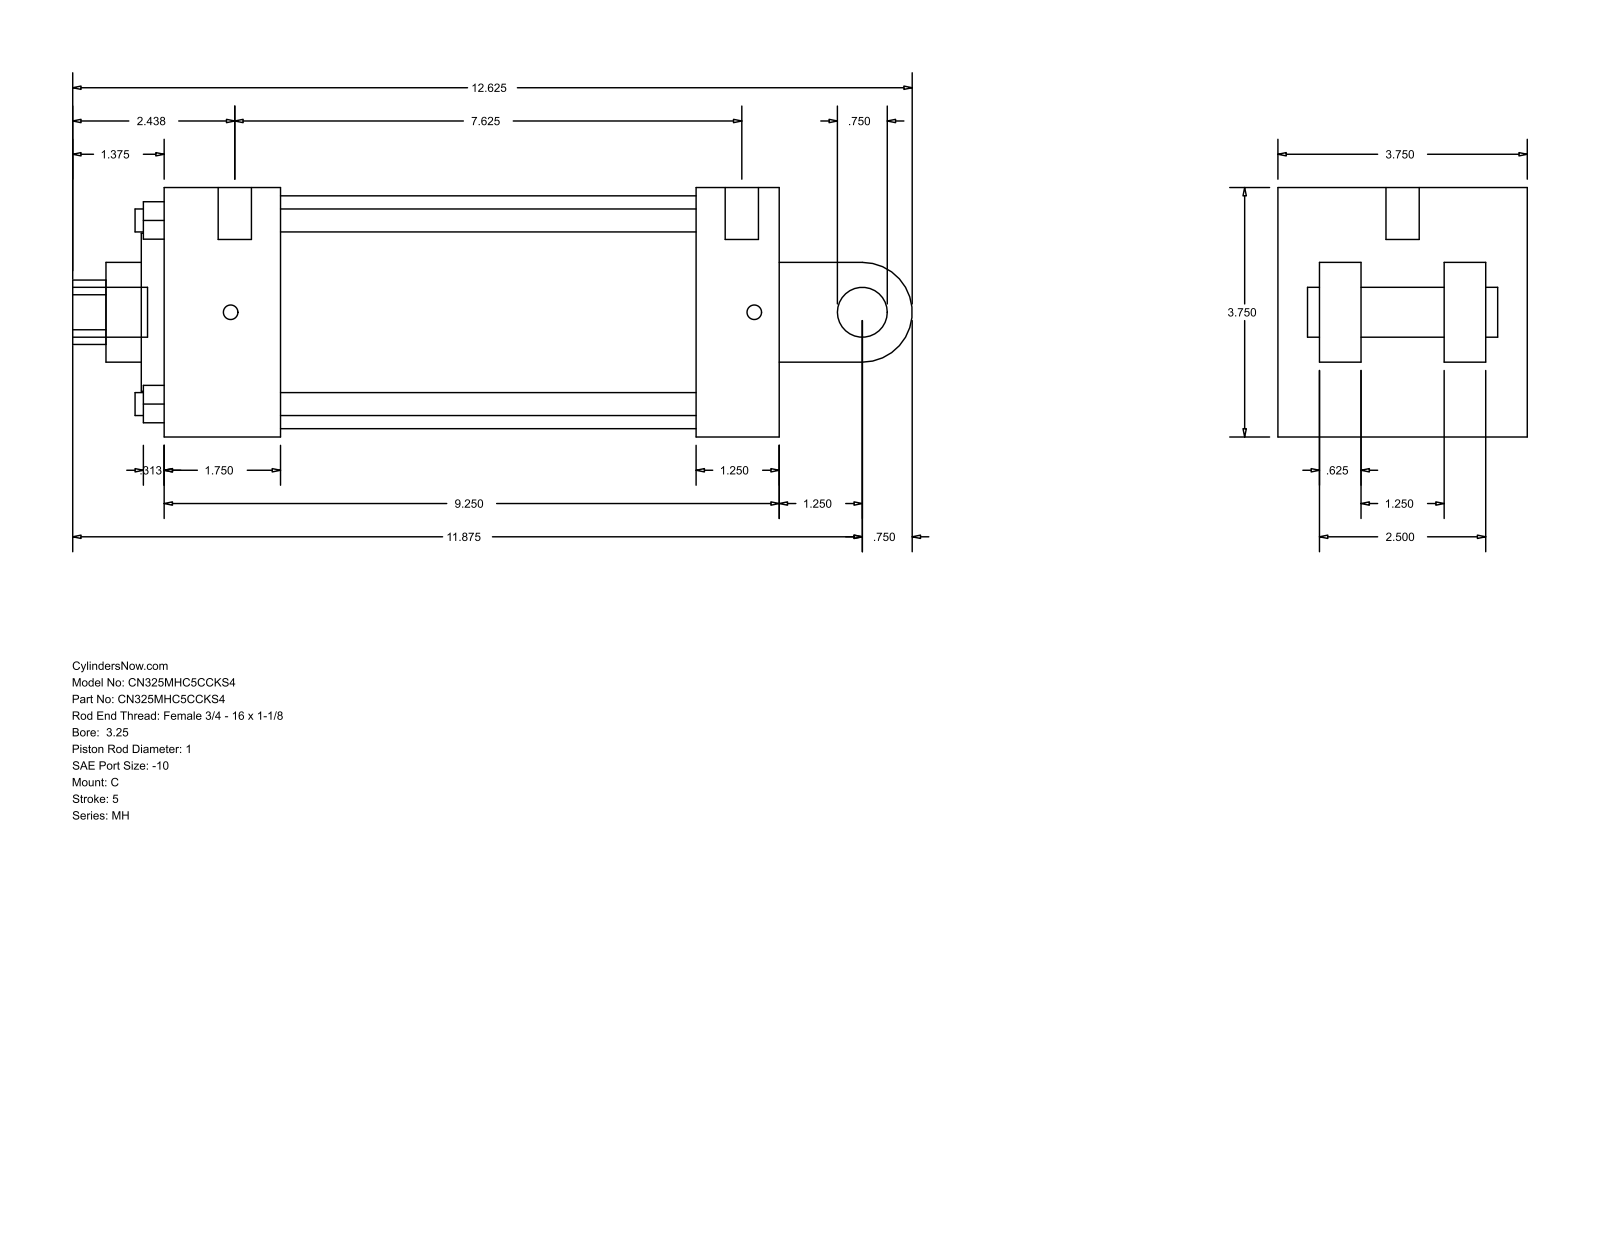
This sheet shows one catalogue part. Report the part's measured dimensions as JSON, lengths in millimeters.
{"part_name": "MH_C__0325_1", "step_written_by": "GSSL Pune (CONFIG_CONTROL_DESIGN)", "units": "millimeters", "bodies": {"solids": 0, "faces": 101, "planar": 71, "cylindrical": 30, "other": 0}, "overall_size": [320.68, 95.25, 95.25], "round_holes": [[8.76, 4], [5.56, 2], [12.7, 1], [25.4, 1], [38.1, 1], [60.33, 1], [88.9, 1]], "round_bosses_or_shafts": [[19.05, 2], [5.56, 2], [12.7, 1]], "partial_cylinders_radius": [[12.29, 1], [19.05, 1]], "face_to_face_distances": [95.24, 15.87, 234.96, 63.5, 31.76, 79.37, 31.74, 47.63, 44.46, 203.2], "hole_center_spacings": [49.57, 70.1, 99.14, 4.76]}
